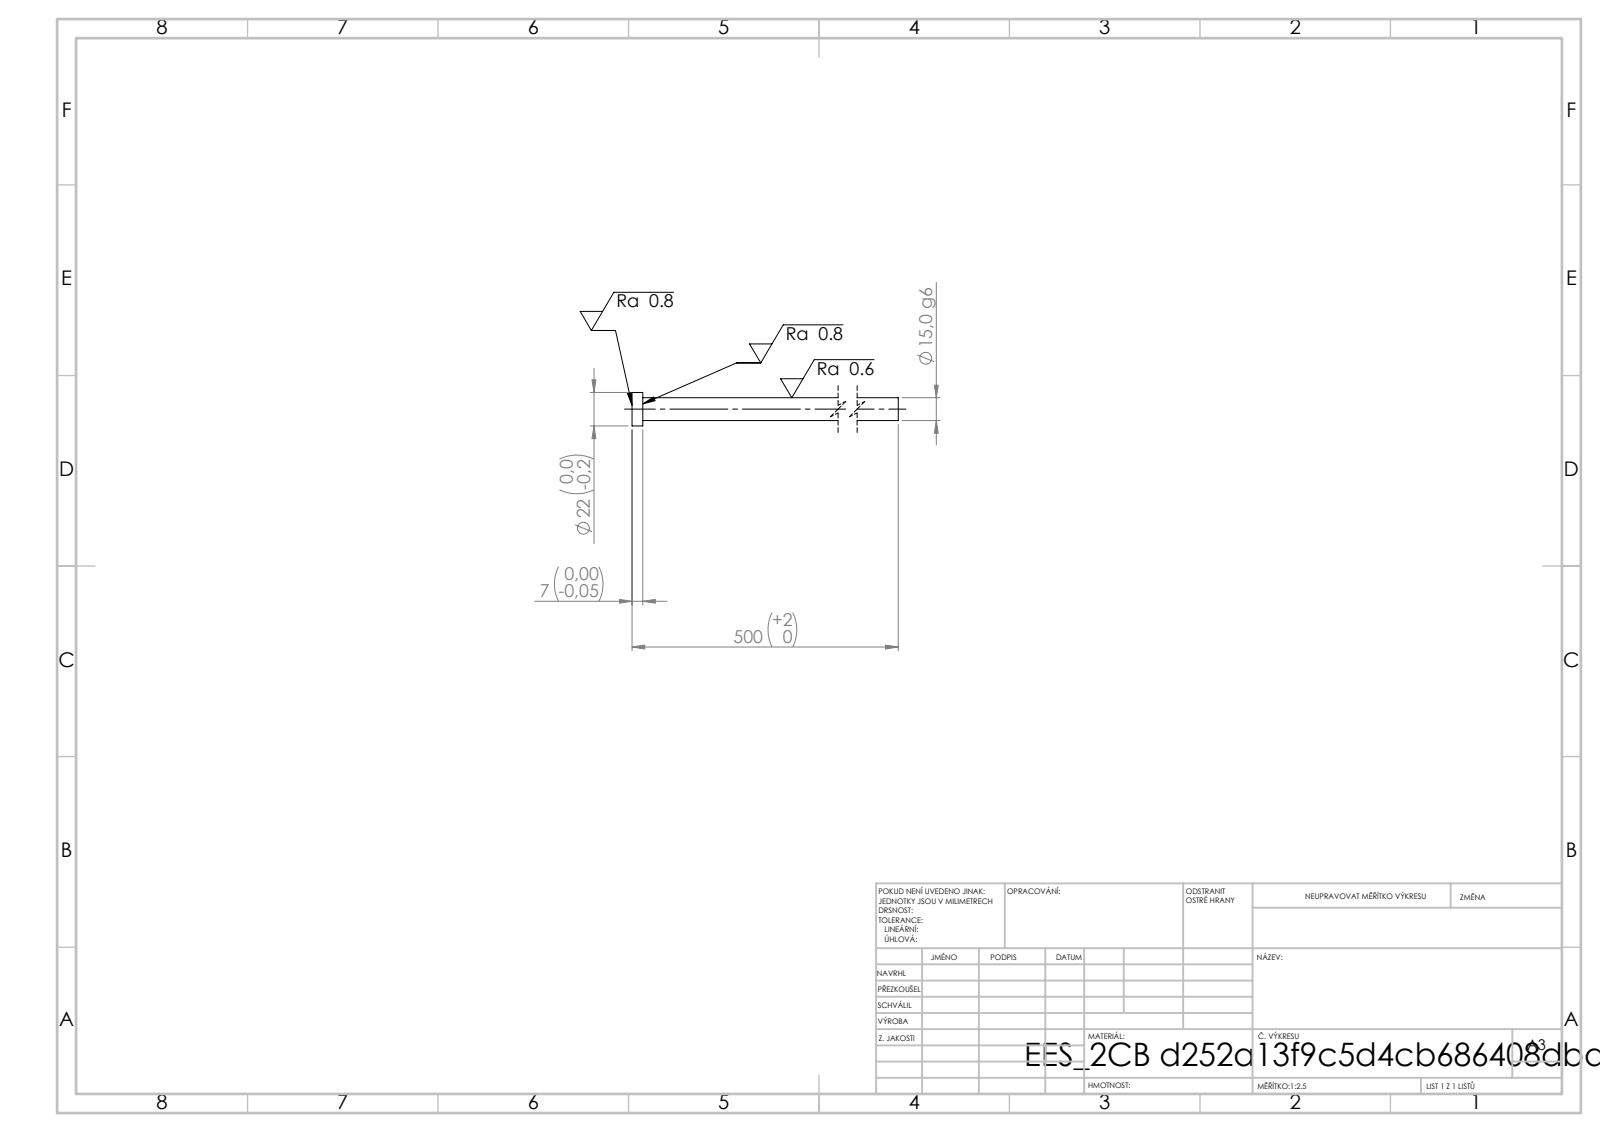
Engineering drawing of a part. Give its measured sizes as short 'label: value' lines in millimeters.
written by: SolidWorks 2019 (CONFIG_CONTROL_DESIGN)
unit: mm
bodies: 1 solid, 7 faces (3 planar, 4 cylindrical, 0 other)
size: 500 × 22 × 22
volume: 89 781 mm³; area: 24 476 mm²
bosses: 1× ⌀22, 1× ⌀15
face distances: 7, 500, 493
